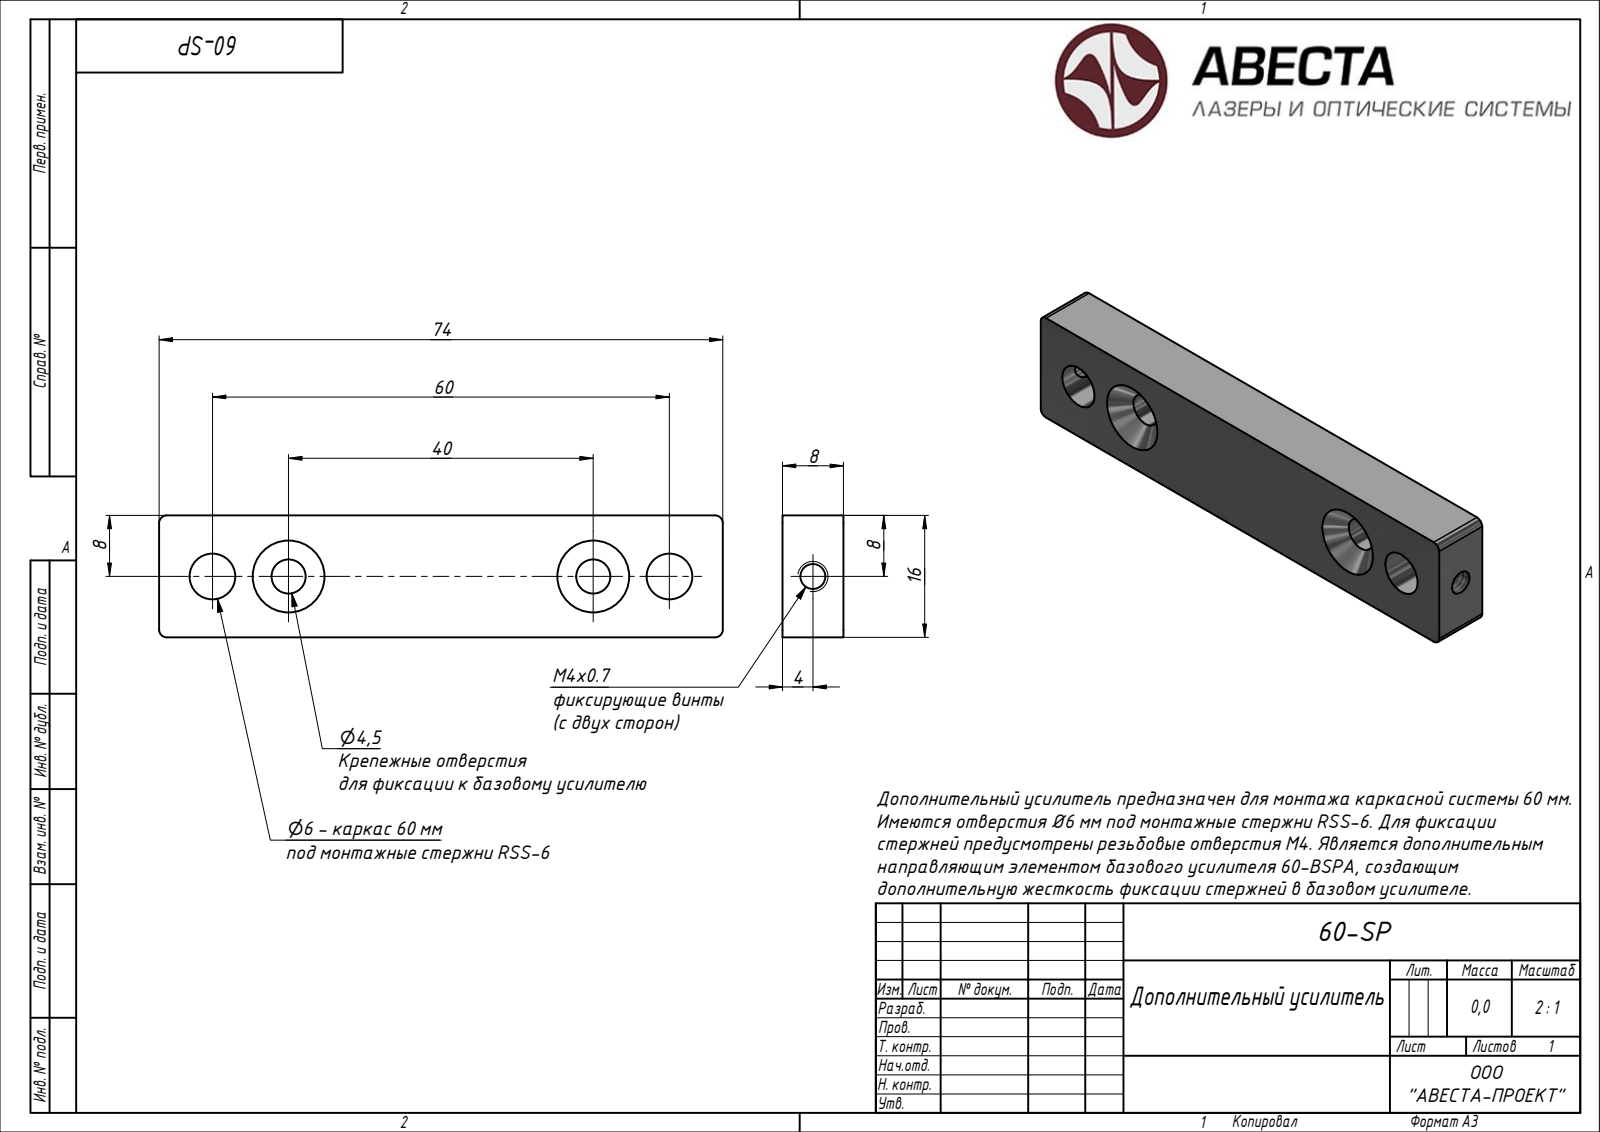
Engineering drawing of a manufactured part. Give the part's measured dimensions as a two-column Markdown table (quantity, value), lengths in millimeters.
| quantity | value |
| --- | --- |
| STEP written by | ST-DEVELOPER v15 (AUTOMOTIVE_DESIGN) |
| units | millimeters |
| bodies | 1 solid, 26 faces (6 planar, 0 cylindrical, 20 other) |
| overall size | 74 × 16 × 8 |
| volume | 8 574 mm³ |
| surface area | 4 172 mm² |
| main face-to-face distances | 8, 16, 74 |
